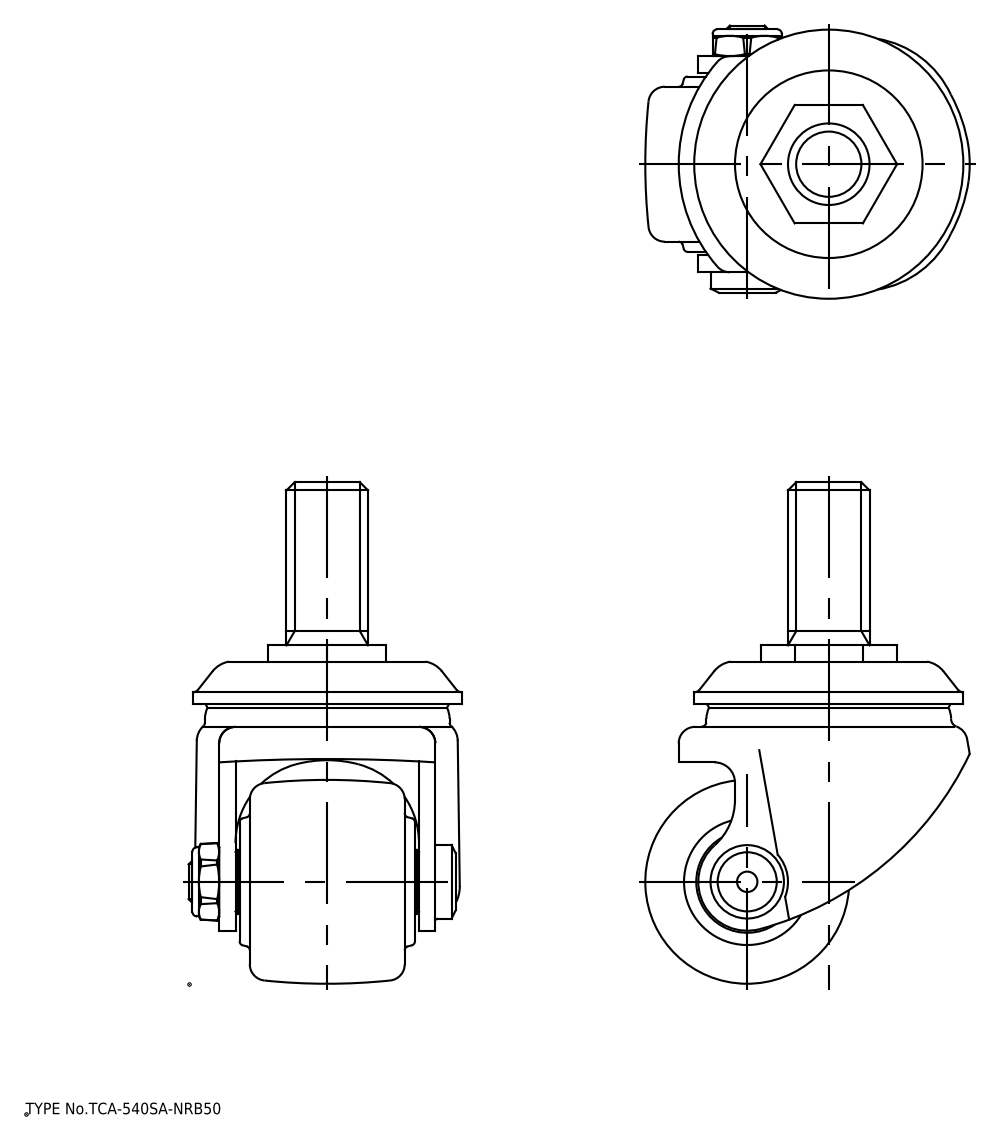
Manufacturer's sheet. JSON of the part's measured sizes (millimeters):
{"part_name": "wheel", "step_written_by": "spGate 19.8.4 (****-****-****-****) (AUTOMOTIVE_DESIGN)", "units": "millimeters", "bodies": {"solids": 2, "faces": 171, "planar": 44, "cylindrical": 49, "other": 78}, "overall_size": [123, 78.73, 69.5], "volume_mm3": 172145, "surface_area_mm2": 38004, "round_holes": [[0.77, 2], [10.2, 1], [22.07, 1], [54.3, 1]], "round_bosses_or_shafts": [[66, 1], [60, 1], [22, 1], [20, 1], [18, 1], [17, 1], [15.6, 1], [10, 1]], "partial_cylinders_radius": [[5, 3], [2, 2], [6, 1], [9.1, 1], [12, 1], [15, 1], [31.5, 1], [80, 1]], "face_to_face_distances": [4, 20, 4.5, 49, 24.5, 7.5, 45.5, 3.5, 41.5, 6.07], "hole_center_spacings": [9, 18]}
